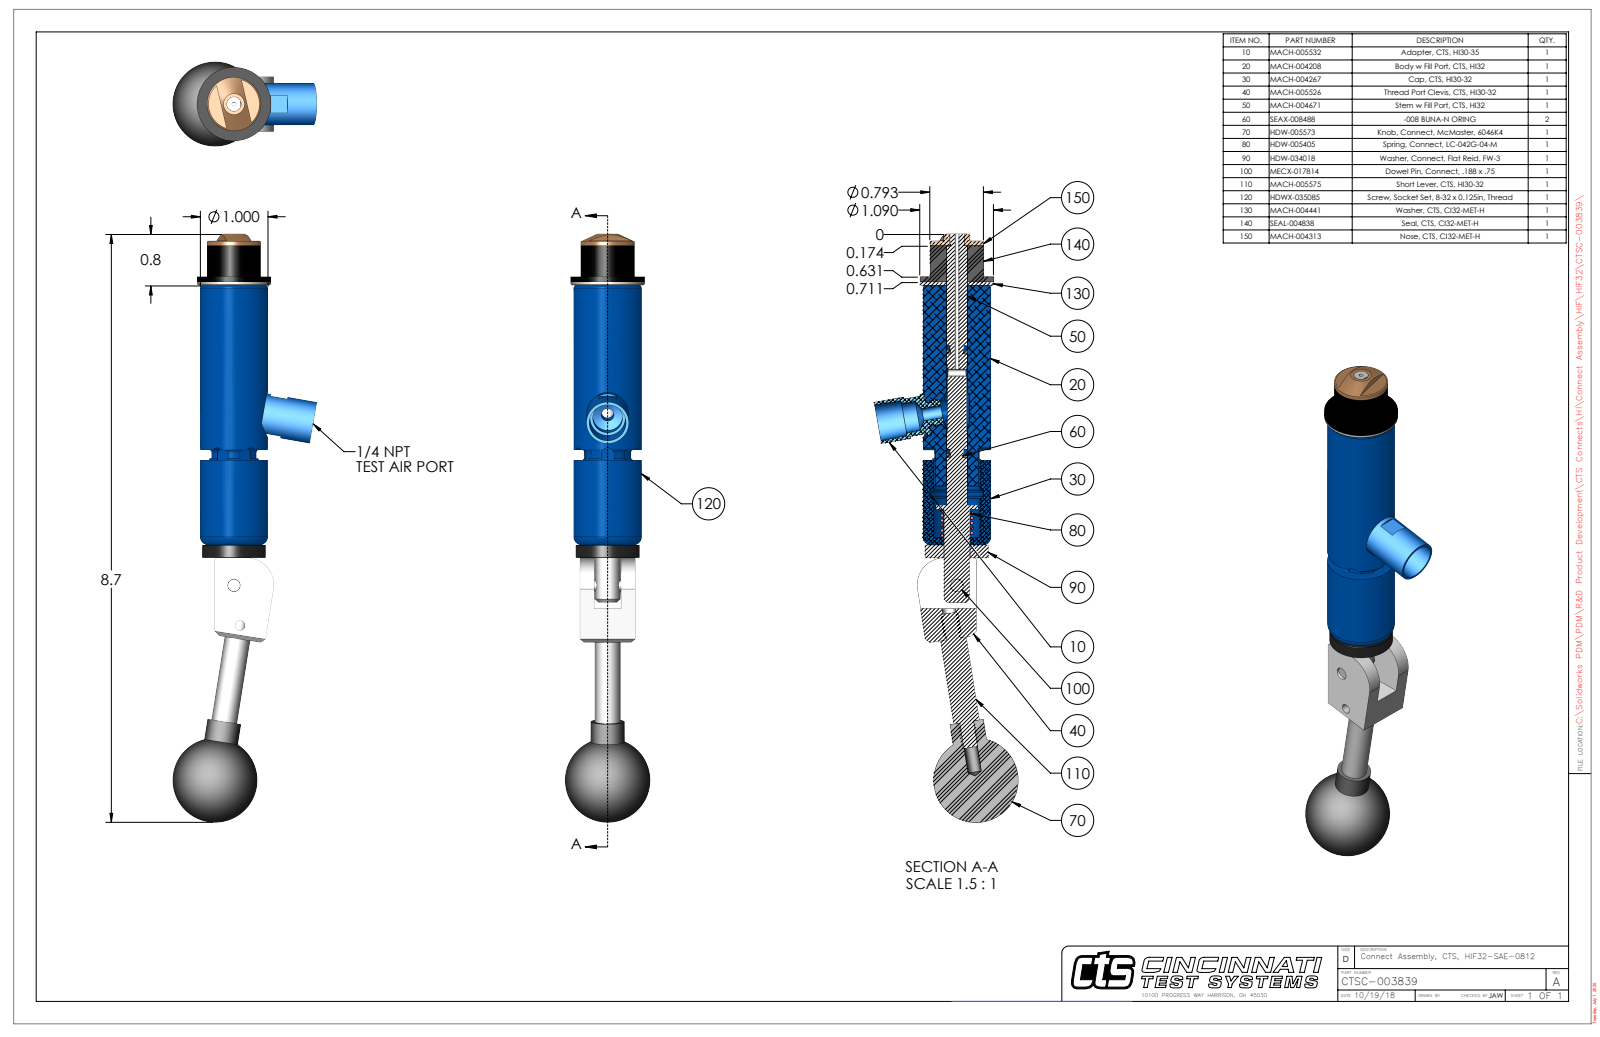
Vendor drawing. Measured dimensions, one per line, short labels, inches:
name: CTSC-003839
written by: SolidWorks 2023 (AUTOMOTIVE_DESIGN)
unit: in
bodies: 9 solids, 298 faces (112 planar, 121 cylindrical, 65 other)
size: 8.692 × 2.128 × 1.25
volume: 5.347 in³; area: 43.01 in²
holes: 2× ⌀0.201, 1× ⌀0.063, 1× ⌀0.109, 1× ⌀0.136, 1× ⌀0.15, 1× ⌀0.187, 1× ⌀0.189, 1× ⌀0.213, 1× ⌀0.31, 1× ⌀0.314, 1× ⌀0.316, 1× ⌀0.385
bosses: 2× ⌀0.25, 2× ⌀0.201, 1× ⌀1.09, 1× ⌀1, 1× ⌀0.936, 1× ⌀0.793, 1× ⌀0.62, 1× ⌀0.5
rounds: 6× R0.093, 2× R0.029, 1× R0.062, 1× R0.325, 1× R0.375, 1× R0.4, 1× R0.478
face distances: 0.05, 0.21, 0.602, 0.537, 0.587, 4.42, 3.883, 3.833, 0.812, 4.608
hole spacings: 0.599, 1.658, 2.252
